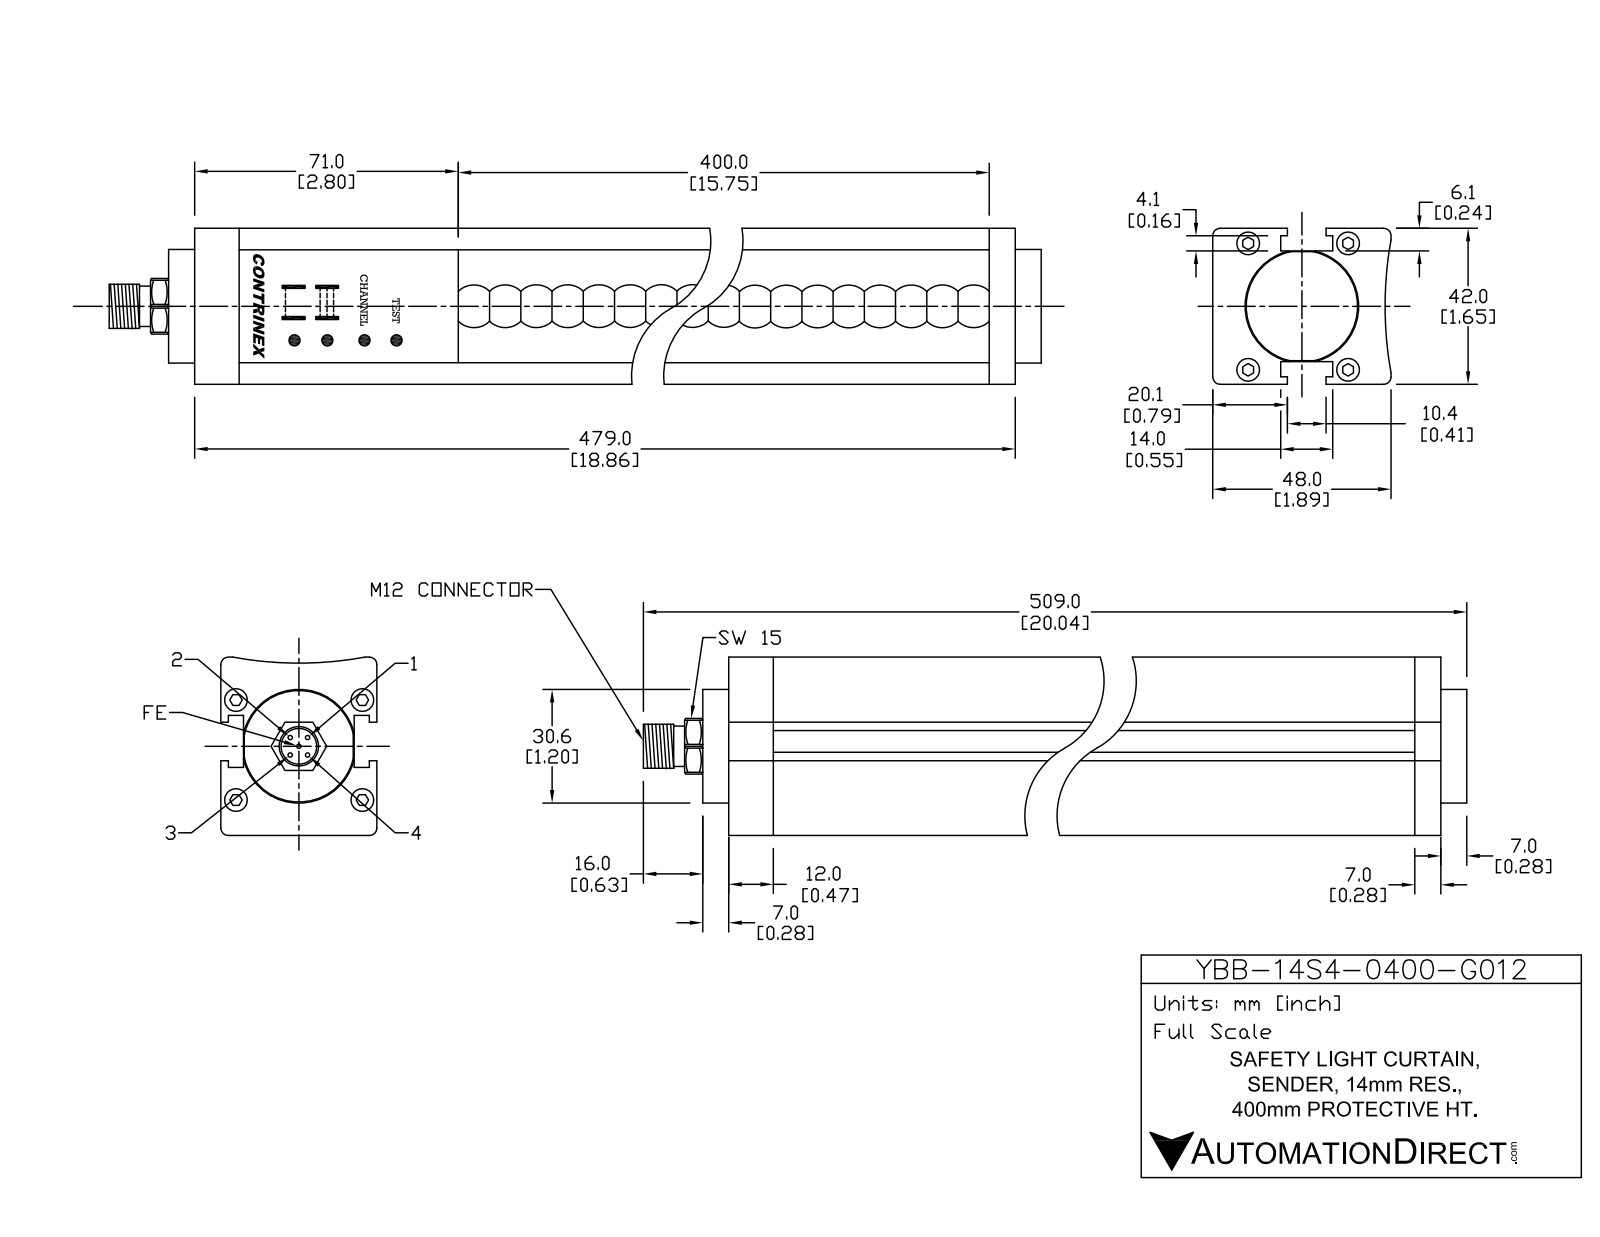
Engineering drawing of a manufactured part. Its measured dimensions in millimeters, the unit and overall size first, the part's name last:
Units: millimetres
Overall size (bounding box): 509 × 48 × 42
Round holes (diameter × count): ⌀6 ×4, ⌀8.5 ×1, ⌀32 ×1
Round bosses / shafts (diameter × count): ⌀1 ×5, ⌀5.5 ×4, ⌀30.6 ×1, ⌀12 ×1, ⌀10.5 ×1
Partial cylindrical surfaces — rounded edges, fillets, slot ends (radius × count): R1 ×48, R0.5 ×4, R0.55 ×2, R8.2 ×1, R100 ×1
Main face-to-face distances: 6.3, 35.7, 42, 29.4, 14, 17.2, 31.2, 459, 15.7, 29.7
Hole centre spacings: 21.04, 22.34, 26.9, 34, 43.35
Volume: 868 060 mm³ · Surface area: 119 957 mm²
Bodies: 19 solids, 440 faces (208 planar, 168 cylindrical, 64 other)
Part name (STEP PRODUCT): YBB-14S4-0400-G012
STEP written by: SolidWorks 2016 (AUTOMOTIVE_DESIGN)
